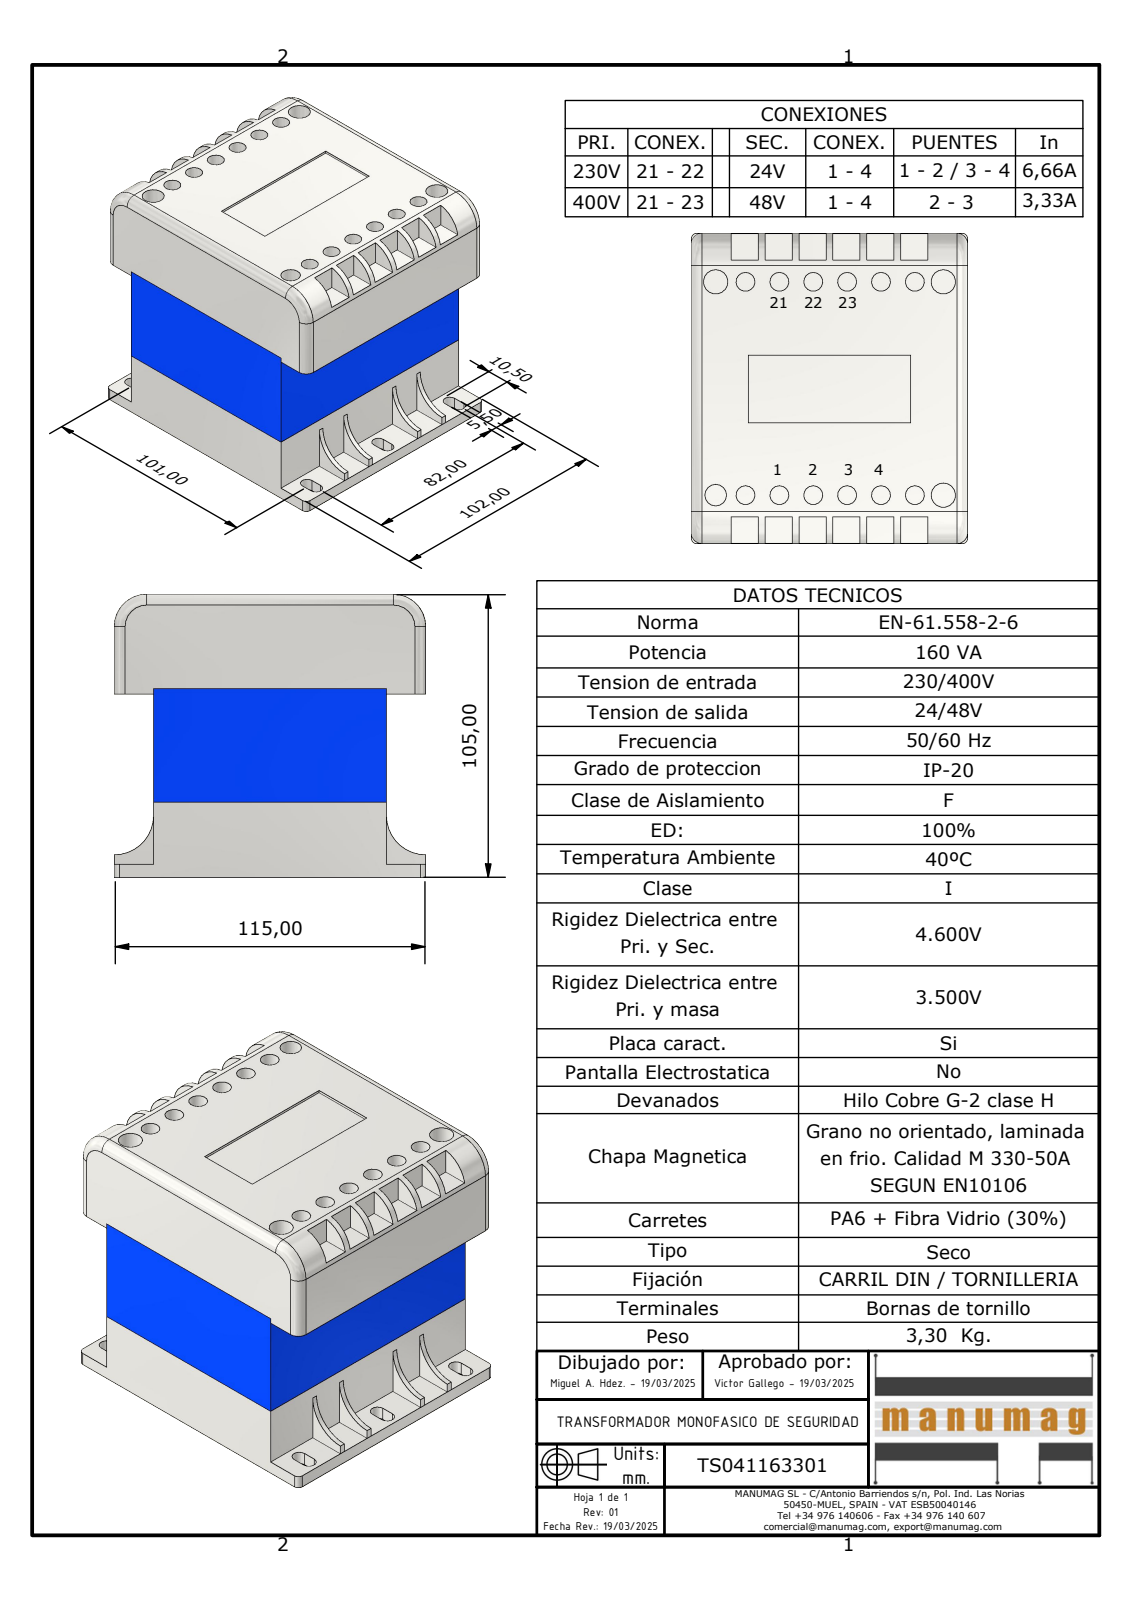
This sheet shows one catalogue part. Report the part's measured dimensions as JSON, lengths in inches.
{"part_name": "TS041163301; INFERIOR EI96; CENTRAL EI96-40; SUPERIOR EI96", "step_written_by": "Autodesk Inventor 2023 (AUTOMOTIVE_DESIGN)", "units": "inches", "bodies": {"solids": 11, "faces": 200, "planar": 152, "cylindrical": 44, "other": 4}, "overall_size": [4.528, 4.134, 4.016], "volume_in3": 29.02, "surface_area_in2": 188, "round_holes": [[0.276, 12], [0.354, 3], [0.315, 1]], "partial_cylinders_radius": [[0.098, 8], [0.157, 6], [0.079, 4], [0.472, 2], [0.571, 2]], "face_to_face_distances": [0.039, 3.346, 3.937, 0.197, 3.976, 2.559, 4.016, 2.756, 4.134, 1.378], "hole_center_spacings": [0.492, 3.149, 0.984, 3.11, 3.262, 1.476, 3.443, 1.969]}
